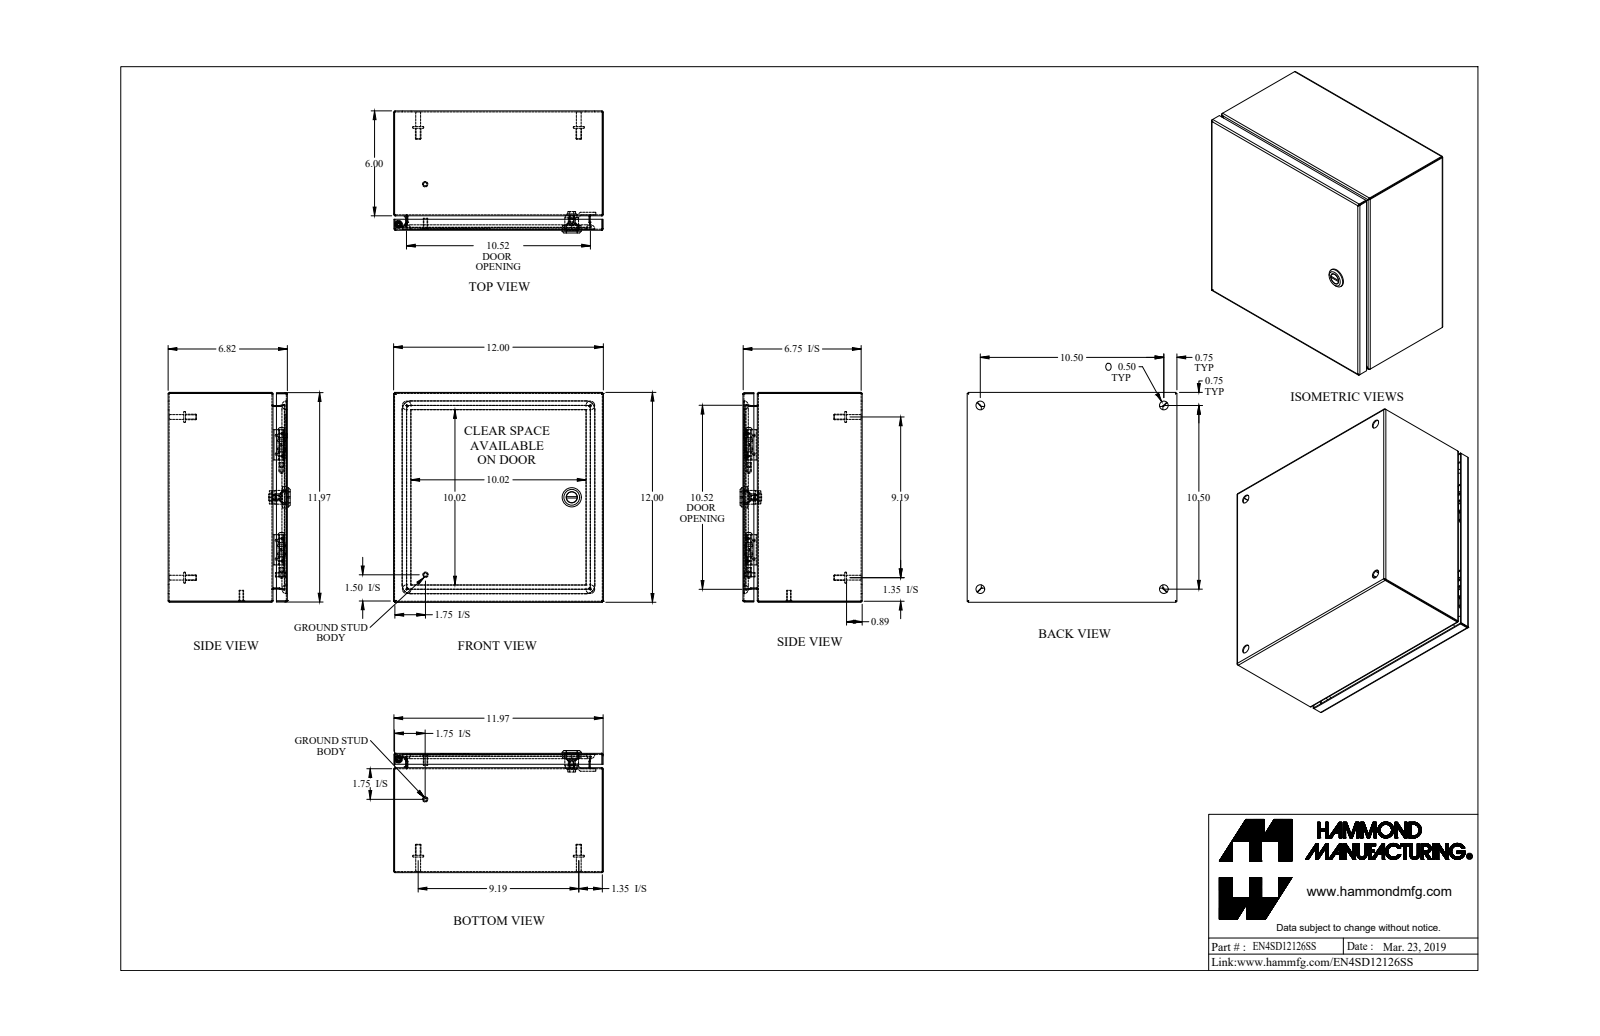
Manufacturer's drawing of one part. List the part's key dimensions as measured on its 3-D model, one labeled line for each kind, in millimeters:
Part name (STEP PRODUCT): EN4SD12126SS_Default
STEP written by: SolidWorks 2019 (CONFIG_CONTROL_DESIGN)
Units: millimetres
Bodies: 22 solids, 657 faces (303 planar, 212 cylindrical, 142 other)
Overall size (bounding box): 304.8 × 304.8 × 177.3
Volume: 708 200 mm³ · Surface area: 936 800 mm²
Round holes (diameter × count): ⌀12.7 ×5, ⌀4.4 ×1, ⌀5 ×1, ⌀6.1 ×1, ⌀6.1 ×1, ⌀9.8 ×1, ⌀16 ×1, ⌀19.5 ×1
Round bosses / shafts (diameter × count): ⌀8 ×6, ⌀15.9 ×5, ⌀7 ×4, ⌀6.4 ×2, ⌀27.9 ×1, ⌀19.9 ×1, ⌀13.3 ×1, ⌀11.6 ×1
Partial cylindrical surfaces — rounded edges, fillets, slot ends (radius × count): R0.7 ×21, R2.2 ×21, R4.8 ×12, R0.2 ×4, R1.6 ×4, R6.4 ×4, R12.7 ×4, R3.2 ×2
Main face-to-face distances: 1.4, 171.8, 303.4, 301.9, 170.4, 173.3, 304.8, 20.9, 151, 152.4
Hole centre spacings: 266.7, 136, 274.4, 377.2
